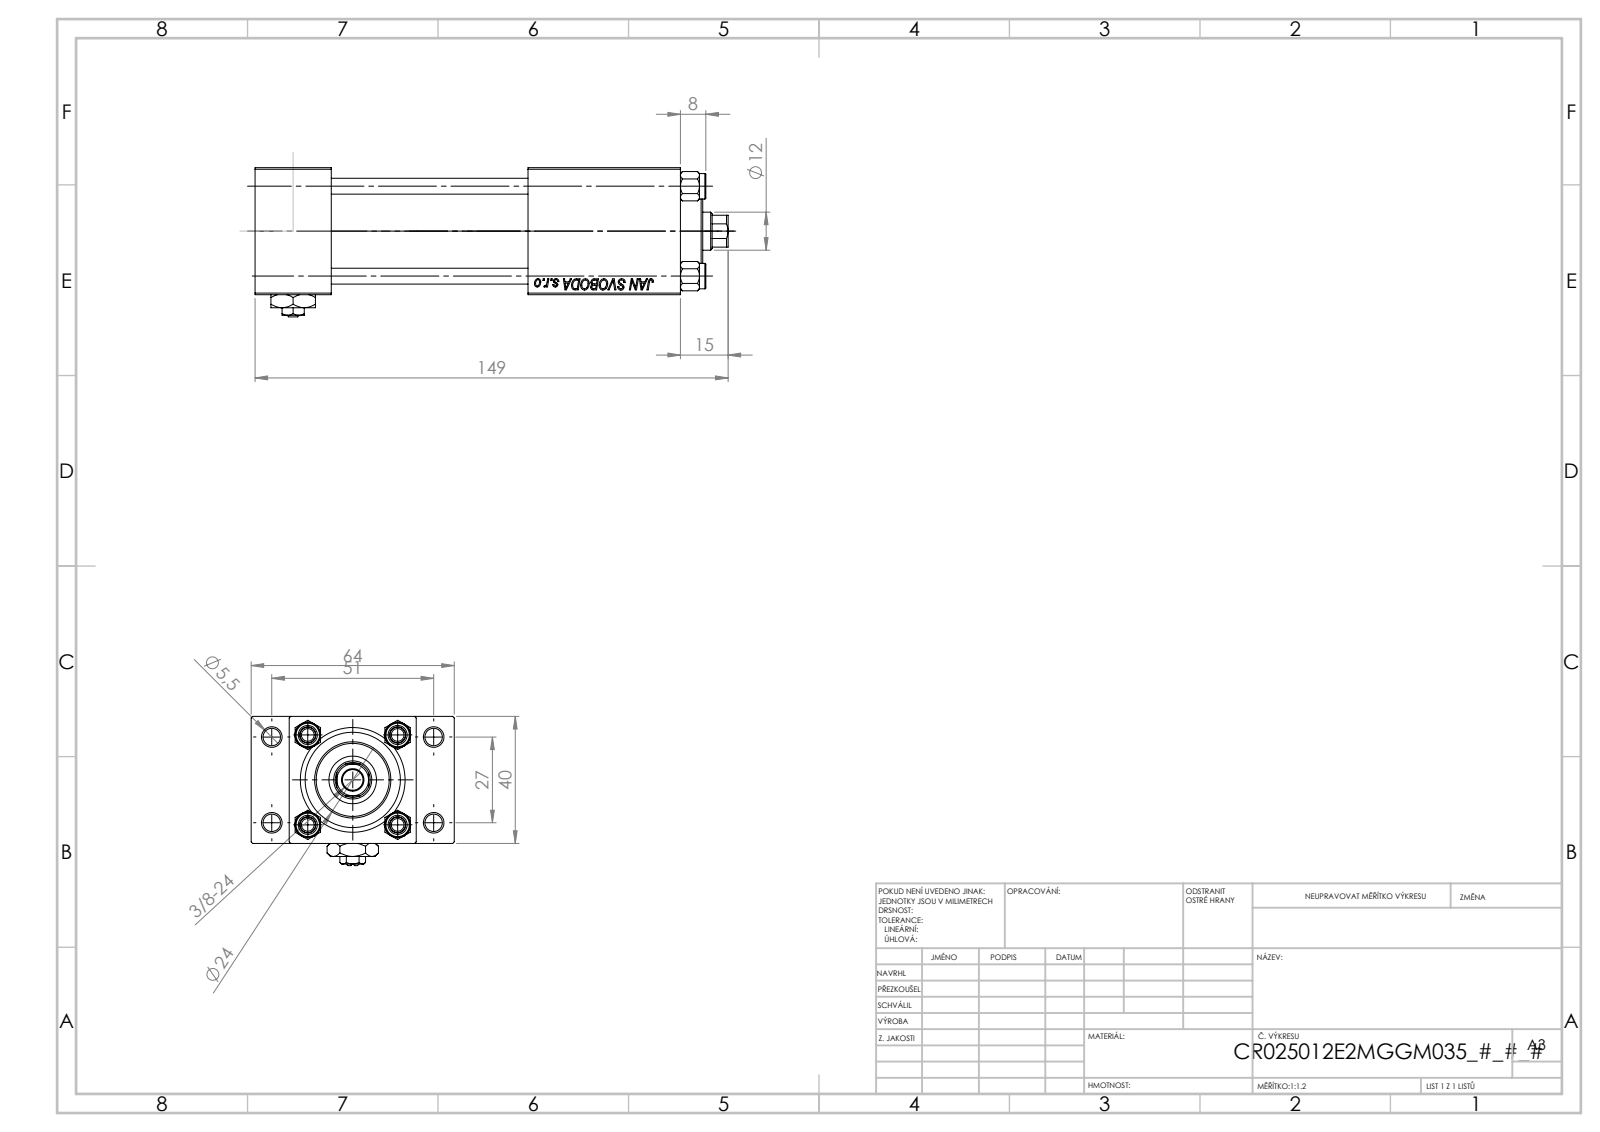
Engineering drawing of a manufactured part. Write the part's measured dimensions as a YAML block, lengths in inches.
part_name: "V215CR_VCP_E; V215_VC_A; Zatka_pro_OIL_PORT; NUT_M5_E (+2 more)"
step_written_by: "SolidWorks 2019 (CONFIG_CONTROL_DESIGN)"
units: inches
bodies: {solids: 12, faces: 1188, planar: 520, cylindrical: 94, other: 574}
overall_size: [5.866, 2.52, 1.85]
volume: 10.35
surface_area: 104.4
round_holes:
  - {diameter: 0.197, count: 4}
  - {diameter: 0.217, count: 4}
  - {diameter: 0.787, count: 3}
  - {diameter: 0.276, count: 2}
  - {diameter: 0.518, count: 2}
  - {diameter: 0.256, count: 1}
  - {diameter: 0.472, count: 1}
  - {diameter: 0.591, count: 1}
  - {diameter: 0.984, count: 1}
  - {diameter: 1.181, count: 1}
round_bosses_or_shafts:
  - {diameter: 0.315, count: 4}
  - {diameter: 1.22, count: 1}
  - {diameter: 0.945, count: 1}
partial_cylinders:
  - {radius: 0.217, count: 1}
face_to_face_distances: [1.575, 0.945, 0.472, 2.047, 5.276, 4.331, 4.146, 3.201, 1.13, 2.52]
hole_center_spacings: [0.448, 0.788, 1.114, 1.136, 1.177, 1.561, 1.903, 1.063]
